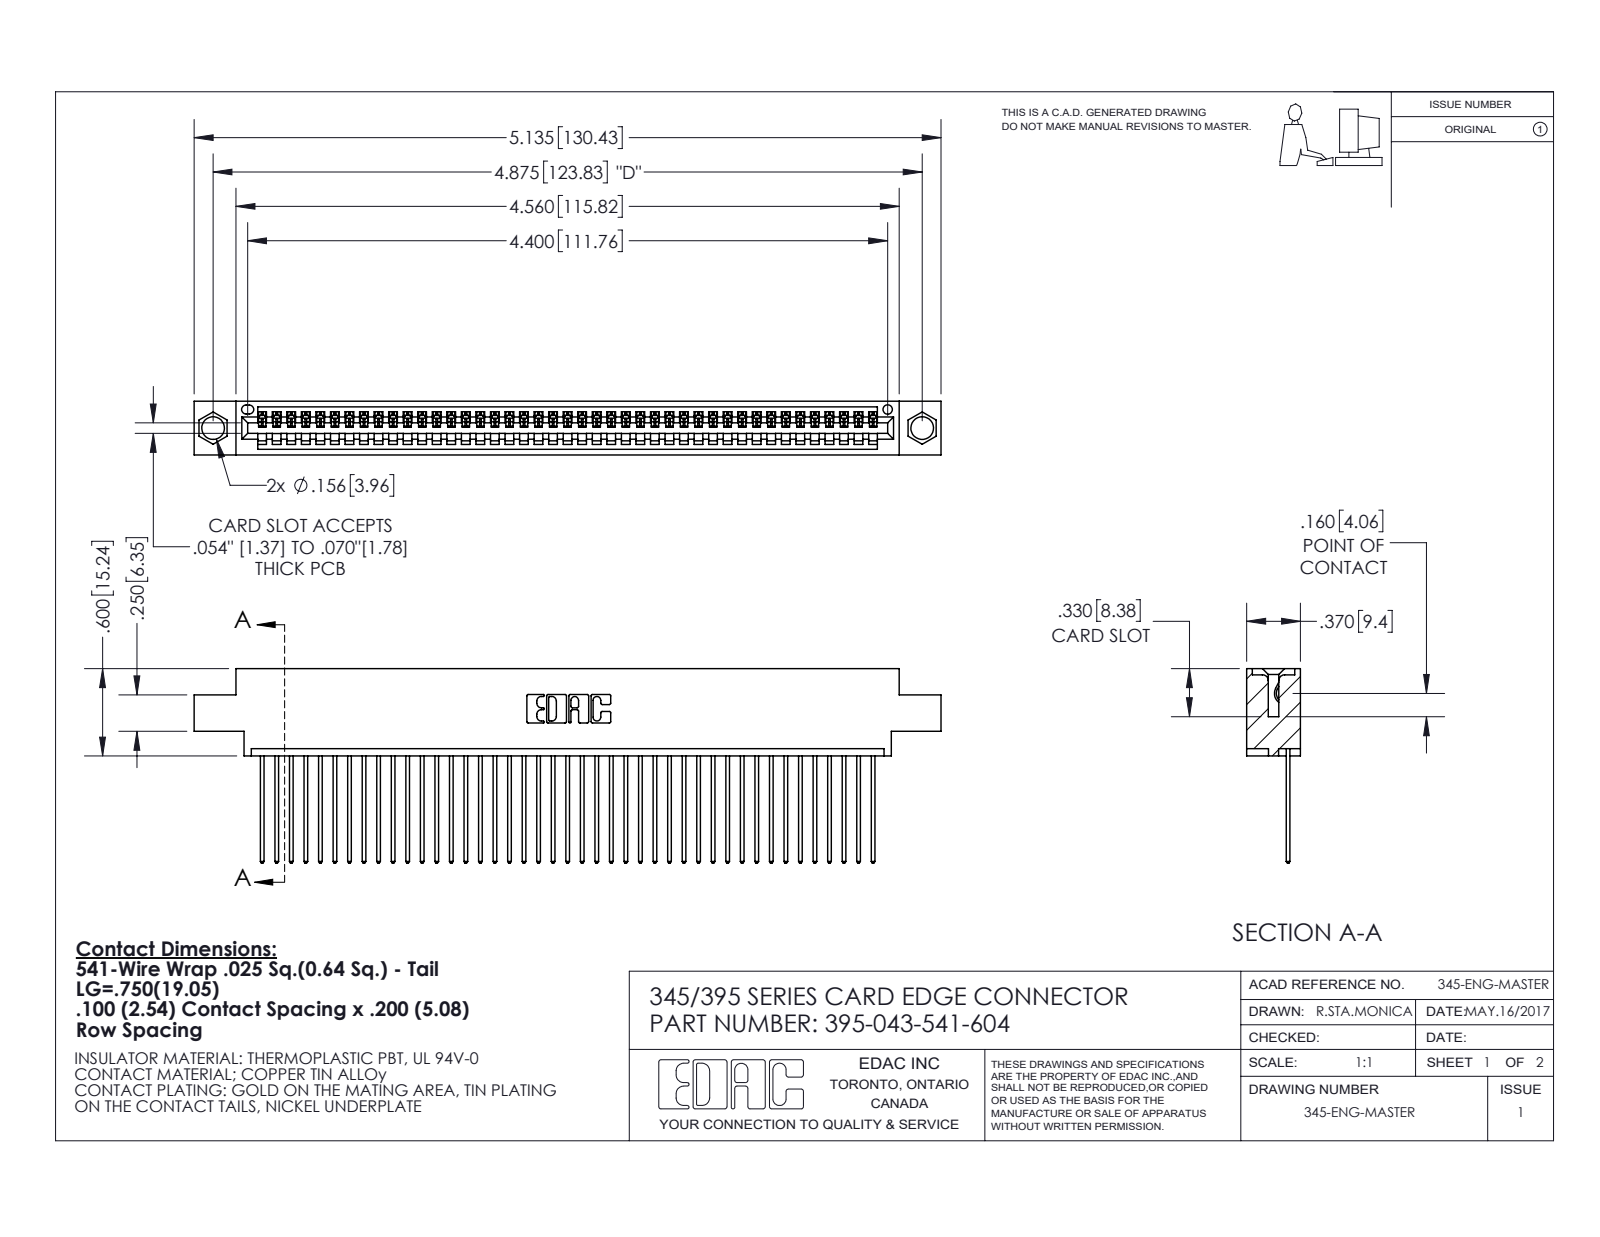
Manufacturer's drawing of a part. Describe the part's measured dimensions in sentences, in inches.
The part is named "345 Part_0.170 Offset - 0.156 Dia-TI; 345-292-001_345-293-141; 395-043-541-604". Its 3-D file was written by "SolidWorks 2020 (CONFIG_CONTROL_DESIGN)". It is 44 solids with 2638 faces: 1818 planar, 820 cylindrical and 0 other. Overall it measures 5.135 by 1.337 by 0.37 inches. Its volume is 0.752 cubic inches and its surface area 26.64 square inches. Round holes: 2 of diameter 0.156, 1 of diameter 0.064. Partial cylindrical surfaces (rounded edges, fillets, slot ends): 86 of radius 0.006, 86 of radius 0.01, 22 of radius 0.01, 6 of radius 0.007, 6 of radius 0.031, 3 of radius 0.026, 2 of radius 0.031, 2 of radius 0.04. The main face-to-face distances are 0.072, 0.298, 0.37, 0.098, 0.272, 0.025, 0.2, 0.225, 0.175, 0.149. The hole center spacings are 0.27, 4.639, 4.875.
